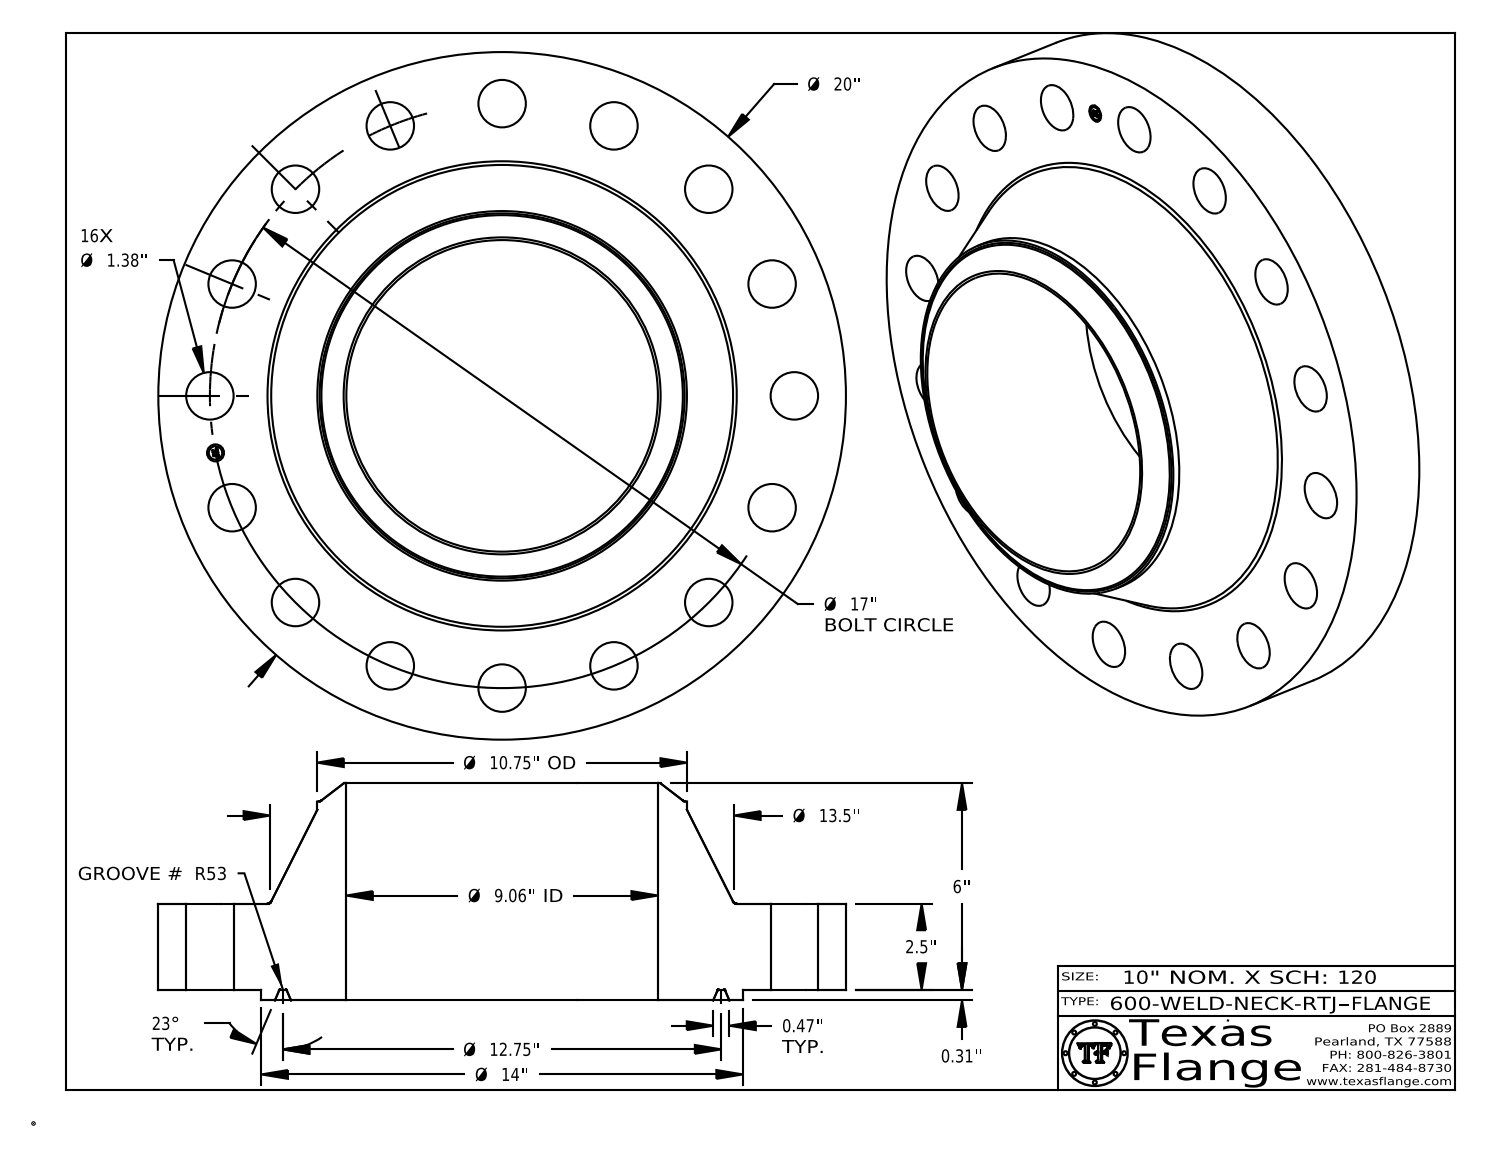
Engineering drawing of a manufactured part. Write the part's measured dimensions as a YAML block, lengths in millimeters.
part_name: "600-WELD-NECK-RTJ"
step_written_by: "CATIA V5 STEP AP214 (AUTOMOTIVE_DESIGN)"
units: millimeters
bodies: {solids: 1, faces: 449, planar: 371, cylindrical: 60, other: 18}
overall_size: [508, 508, 160.4]
volume: 12160000
surface_area: 689700
round_holes:
  - {diameter: 35.1, count: 16}
  - {diameter: 12.6, count: 1}
  - {diameter: 230.2, count: 1}
round_bosses_or_shafts:
  - {diameter: 0.8, count: 8}
  - {diameter: 508, count: 1}
  - {diameter: 355.6, count: 1}
  - {diameter: 273.1, count: 1}
  - {diameter: 9.9, count: 1}
face_to_face_distances: [63.5, 8, 71.5, 160.4, 152.4, 88.9, 71.1, 63.1, 0.4, 89.3]
hole_center_spacings: [84.3, 359, 215.9, 165.3, 305.3, 239.9, 239.9, 398.9]
